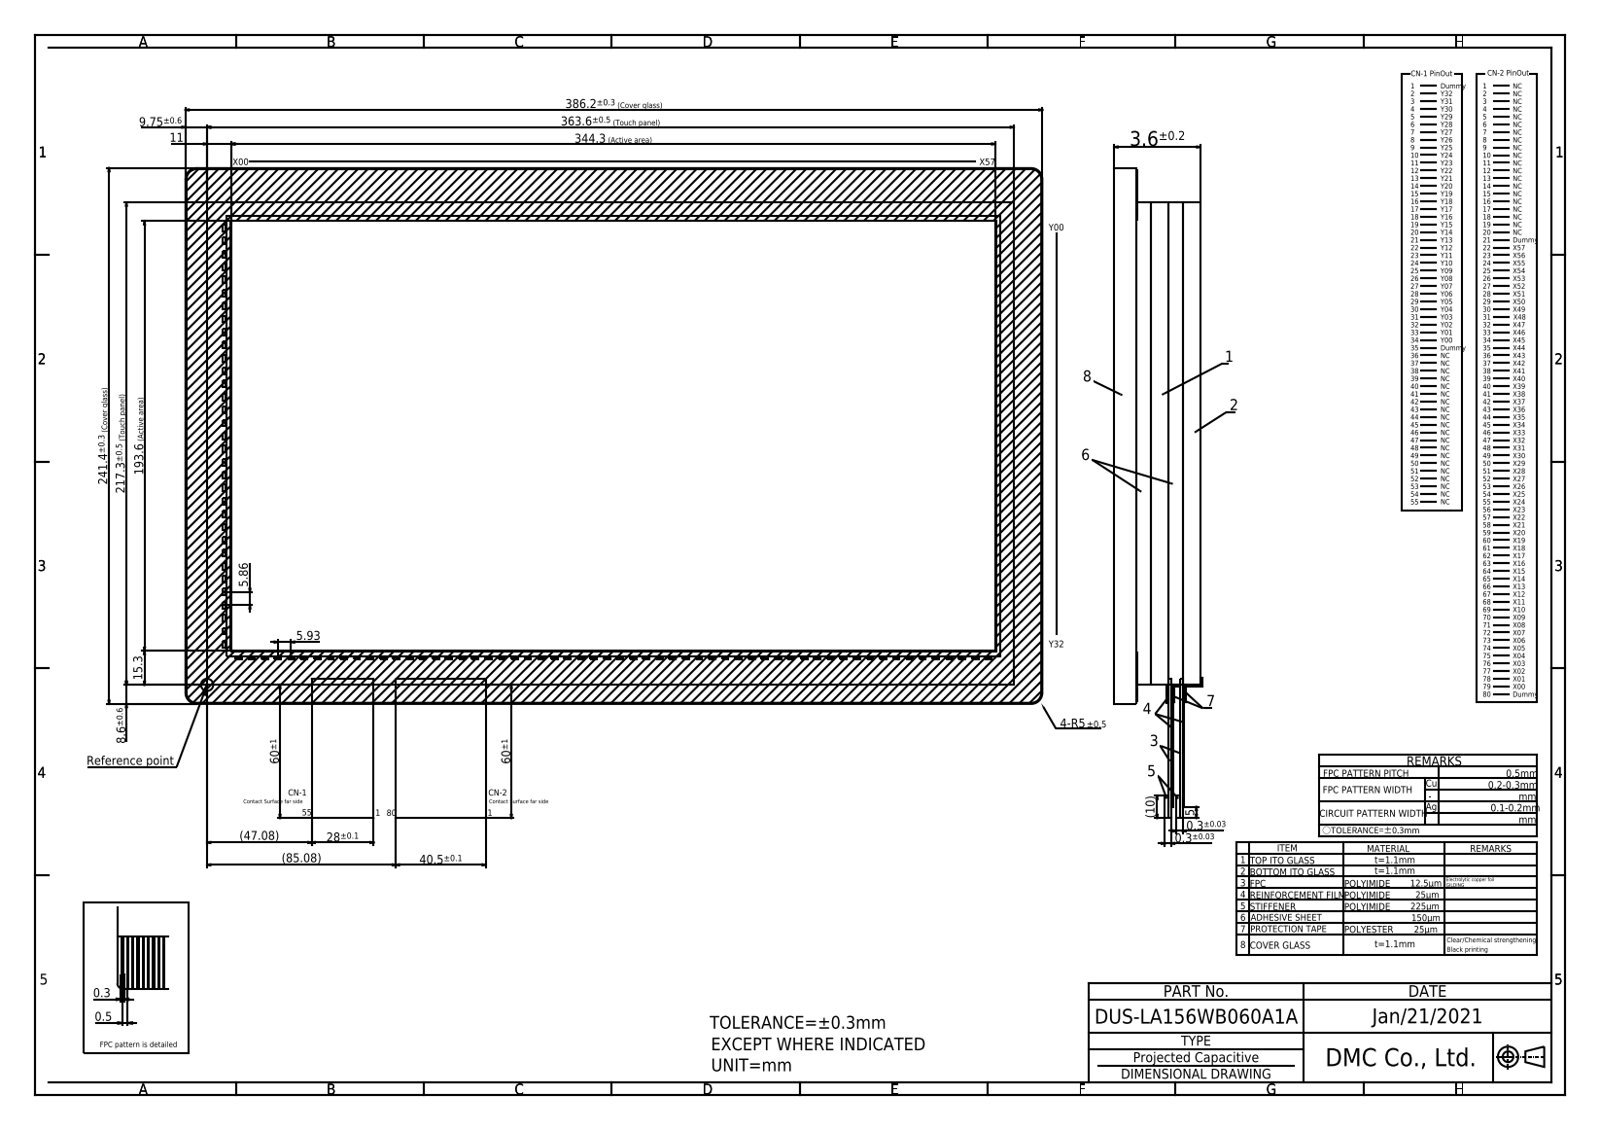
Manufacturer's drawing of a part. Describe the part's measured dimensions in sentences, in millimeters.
The part is named "DUS-LA156WB060A1A". Its 3-D file was written by "Autodesk Inventor 2020 (CONFIG_CONTROL_DESIGN)". It is 1 solid with 584 faces: 576 planar, 8 cylindrical and 0 other. Overall it measures 540.68 by 341.08 by 3.6 millimeters. Its volume is 293 969 cubic millimeters and its surface area 332 419 square millimeters. Partial cylindrical surfaces (rounded edges, fillets, slot ends): 4 of radius 0.2, 4 of radius 5. The main face-to-face distances are 1.1, 2.5, 3.6, 1.2, 2.4, 1.25, 1.15, 1.35, 2.45, 2.35.
